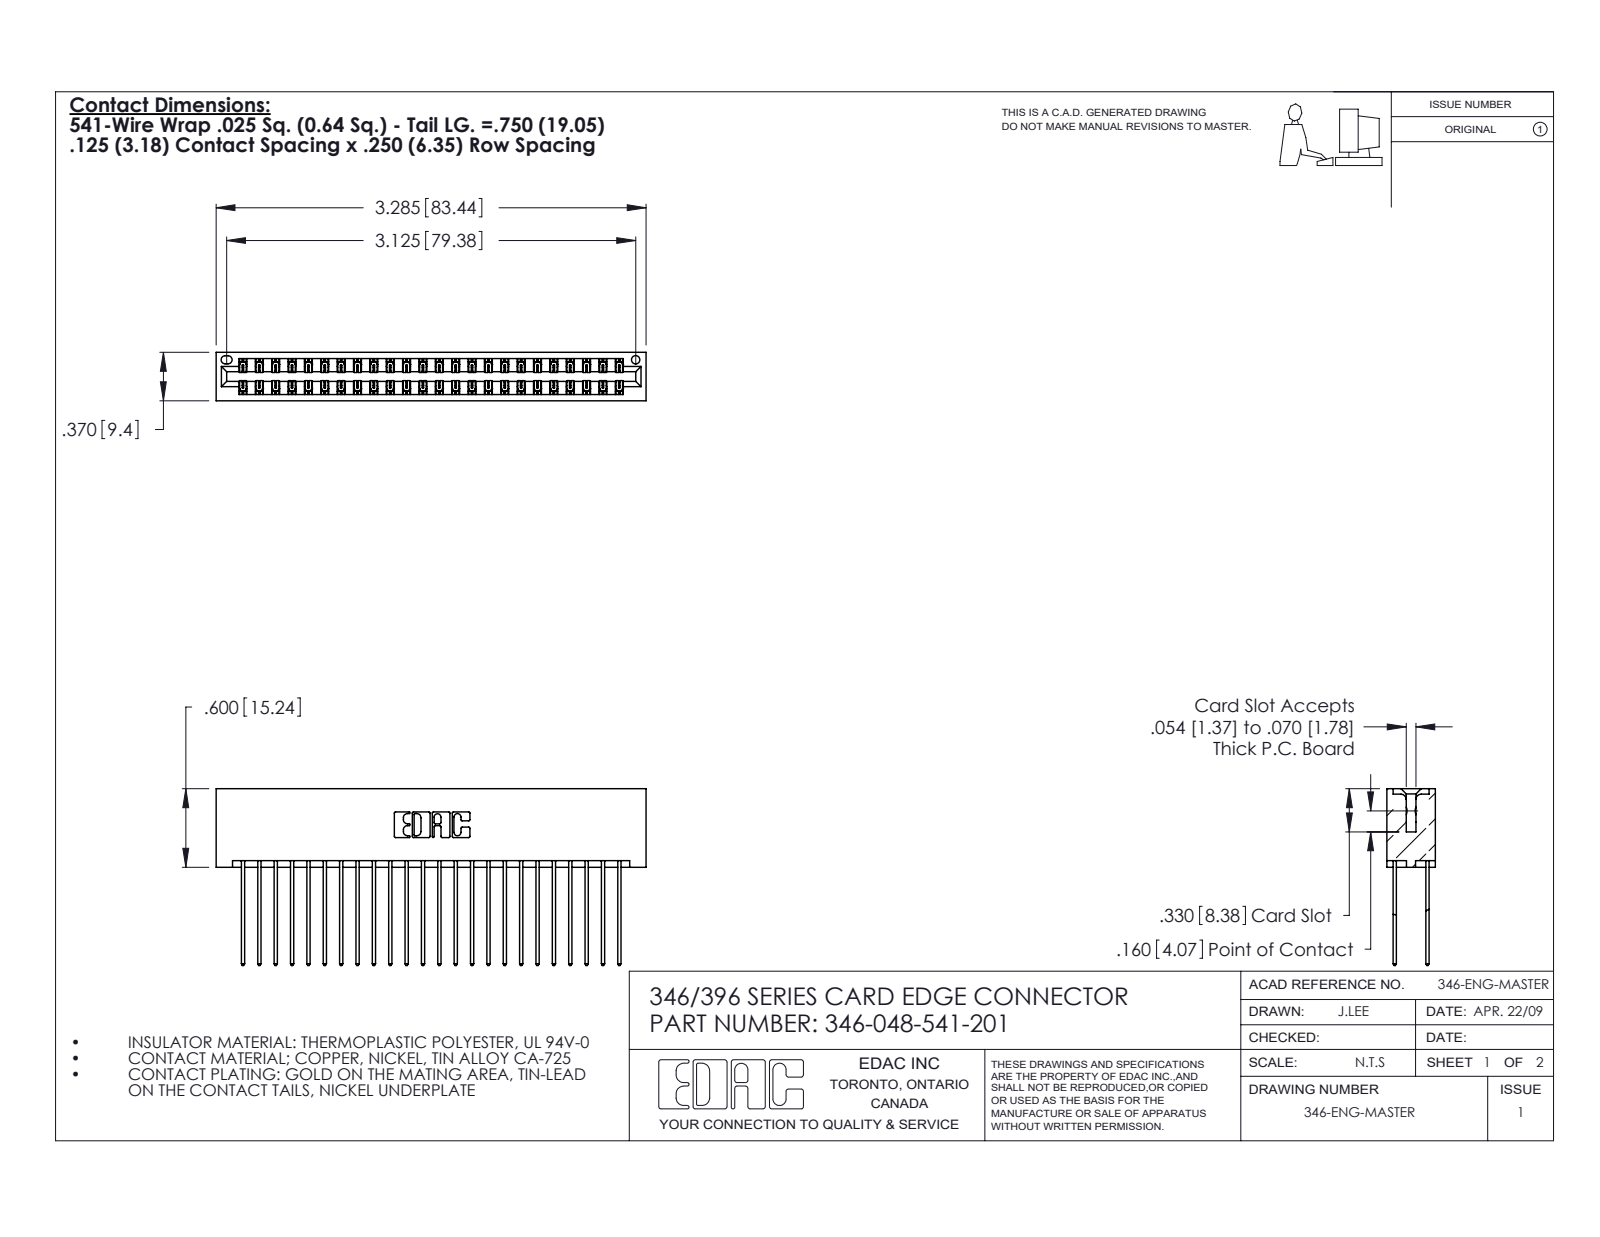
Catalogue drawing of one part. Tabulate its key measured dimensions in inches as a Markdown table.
| quantity | value |
| --- | --- |
| part name | 345-292-001_345-293-141; 346-048-541-201; 346 Part_No Mounting Lugs |
| STEP written by | SolidWorks 2020 (CONFIG_CONTROL_DESIGN) |
| units | inches |
| bodies | 49 solids, 2610 faces (1752 planar, 858 cylindrical, 0 other) |
| overall size | 3.285 × 1.35 × 0.37 |
| volume | 0.54 in³ |
| surface area | 20.71 in² |
| round holes (diameter × count) | 0.064 × 1 |
| partial cylindrical surfaces (radius × count) | 0.006 × 72, 0.01 × 48, 0.01 × 22, 0.007 × 6, 0.031 × 6, 0.026 × 3, 0.014 × 2, 0.022 × 2 |
| main face-to-face distances | 0.048, 0.322, 0.25, 0.072, 0.298, 0.025, 0.37, 0.275, 0.225, 0.148 |
